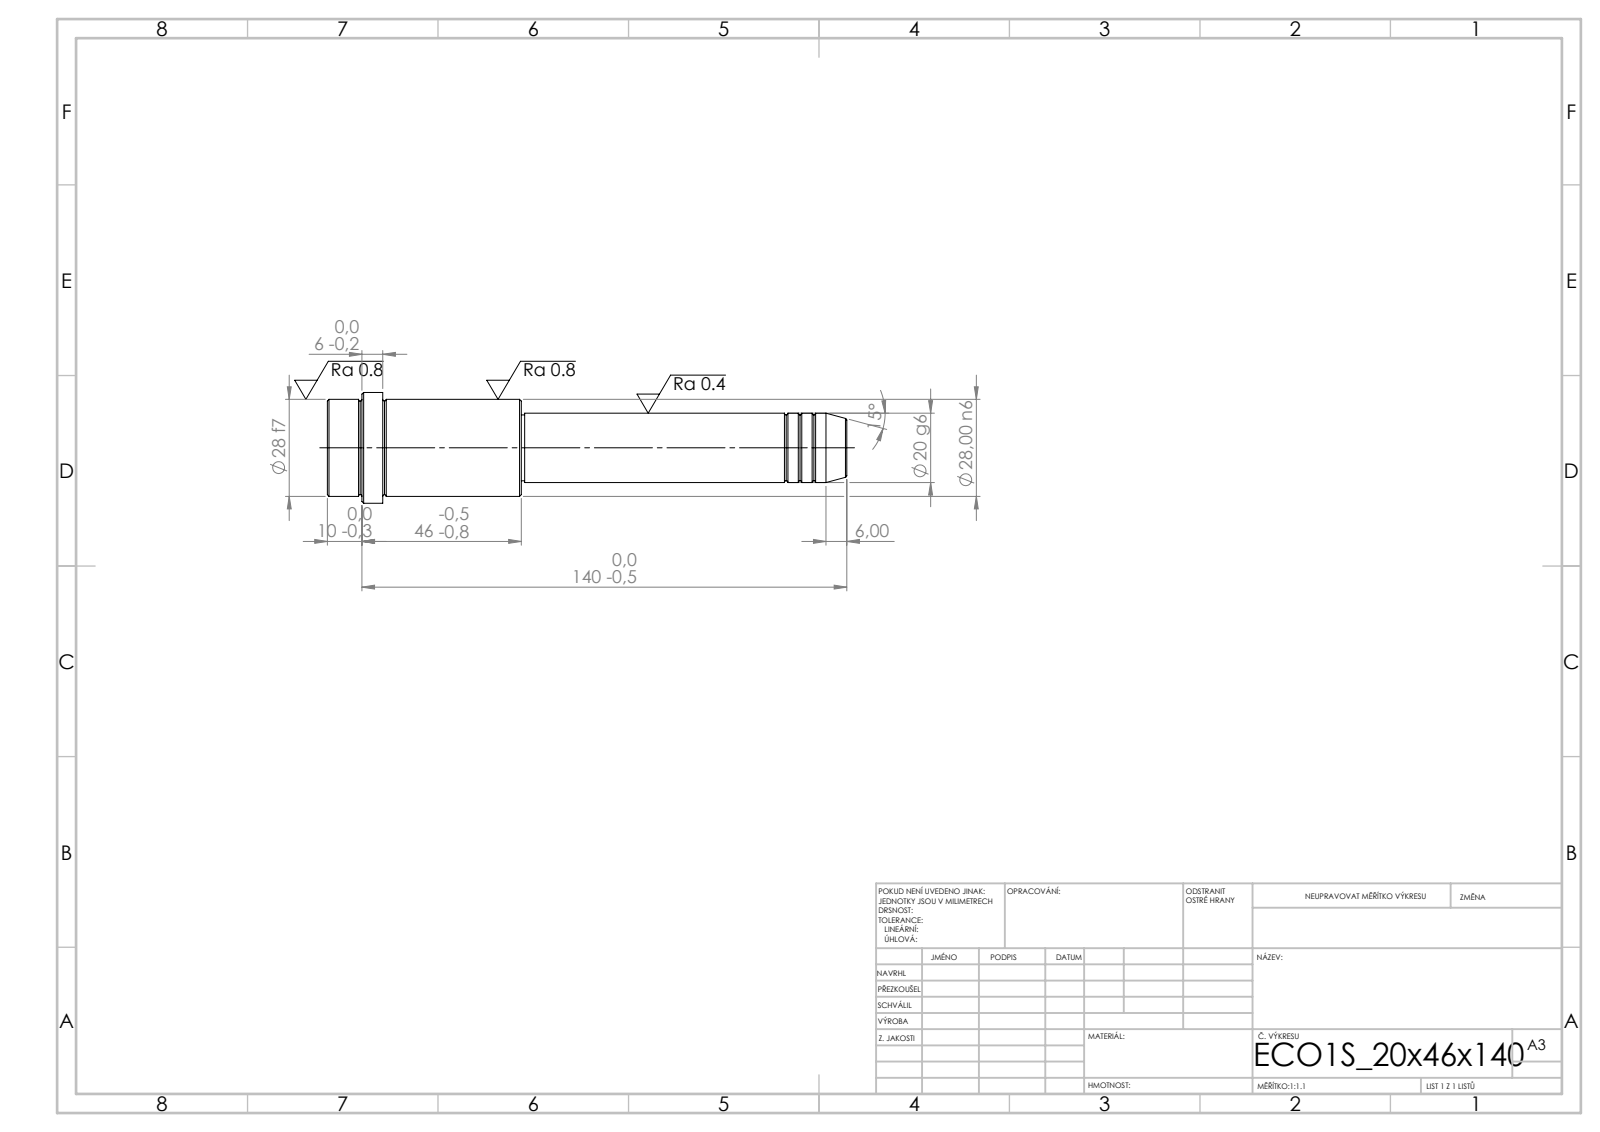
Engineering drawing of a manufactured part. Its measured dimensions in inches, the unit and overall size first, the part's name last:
Units: inches
Overall size (bounding box): 5.906 × 1.26 × 1.26
Round bosses / shafts (diameter × count): ⌀1.26 ×1, ⌀1.102 ×1, ⌀0.787 ×1, ⌀0.748 ×1
Main face-to-face distances: 2.205, 3.701, 5.906, 5.276, 1.575, 0.63, 5.512, 1.811, 0.236, 0.394
Volume: 3.945 in³ · Surface area: 19.48 in²
Bodies: 1 solid, 52 faces (6 planar, 16 cylindrical, 30 other)
STEP written by: SolidWorks 2019 (CONFIG_CONTROL_DESIGN)
